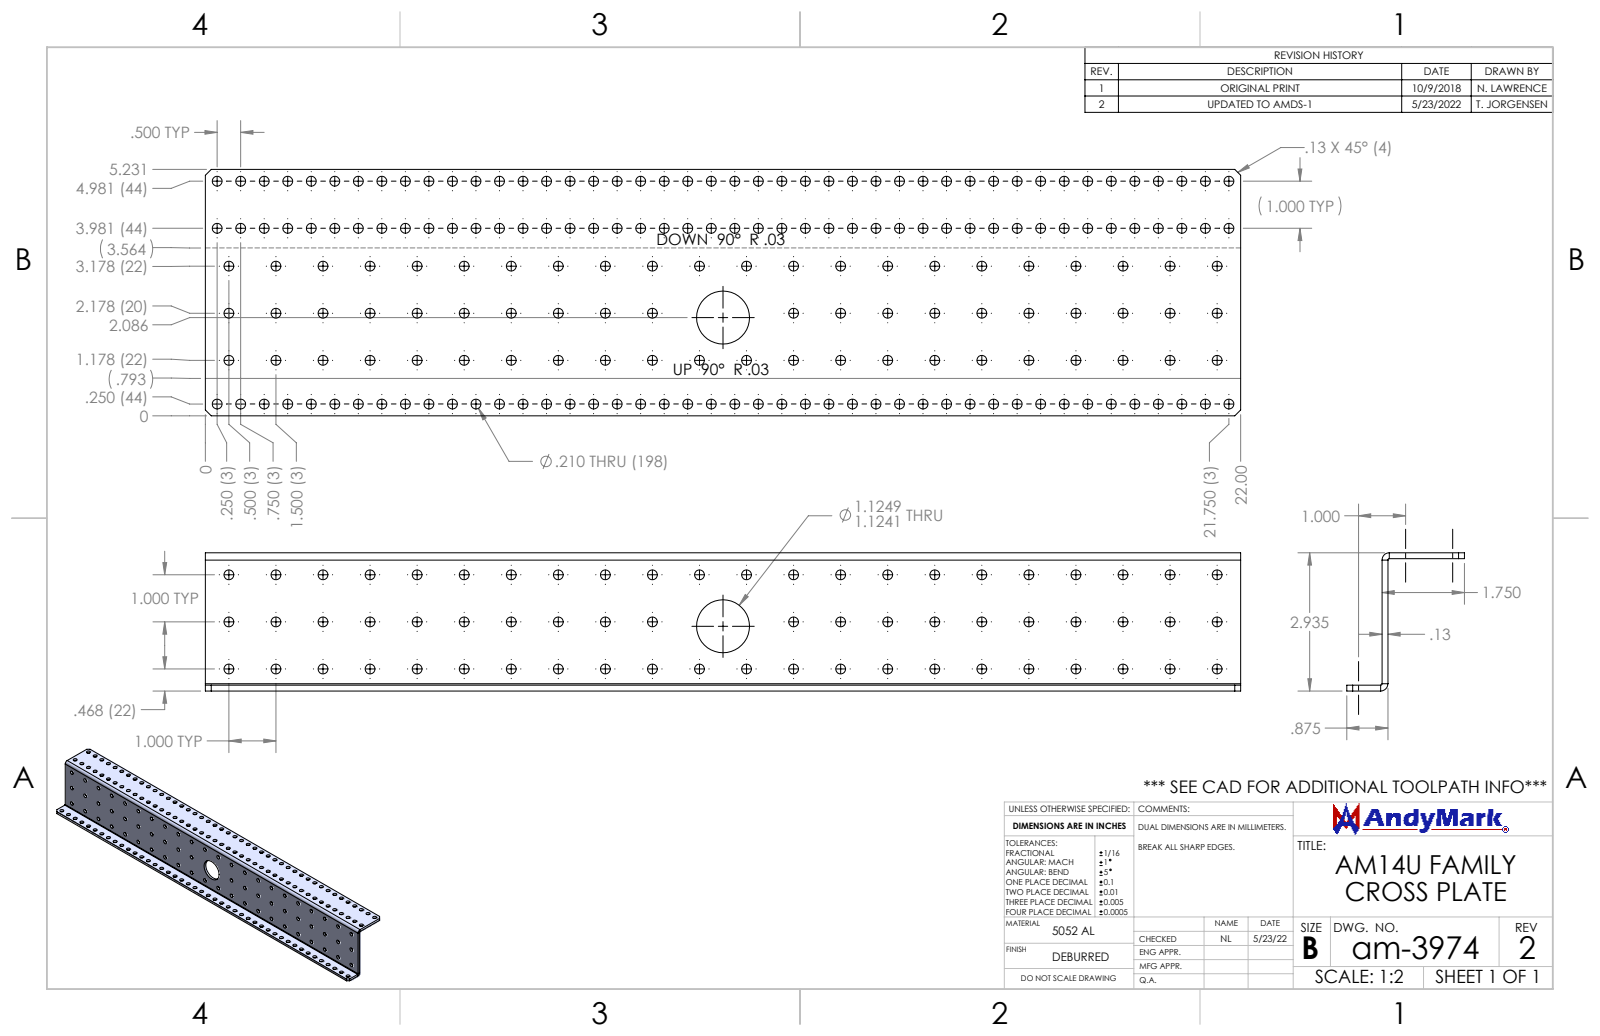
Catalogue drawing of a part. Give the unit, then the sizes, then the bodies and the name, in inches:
Units: inches
Overall size (bounding box): 22 × 2.935 × 2.5
Round holes (diameter × count): ⌀0.21 ×196, ⌀1.125 ×1
Partial cylindrical surfaces — rounded edges, fillets, slot ends (radius × count): R0.029 ×2, R0.154 ×2
Main face-to-face distances: 0.125, 0.125, 2.685, 2.81, 2.81, 2.935, 1.625, 1.75, 2.5, 0.875
Hole centre spacings: 1, 2.236, 1.414, 2, 3.162, 1.118, 3, 4.123
Volume: 13.41 in³ · Surface area: 237.9 in²
Bodies: 1 solid, 420 faces (22 planar, 398 cylindrical, 0 other)
Part name (STEP PRODUCT): am-3974 AM14U Family Cross Plate
STEP written by: SolidWorks 2021 (CONFIG_CONTROL_DESIGN)
